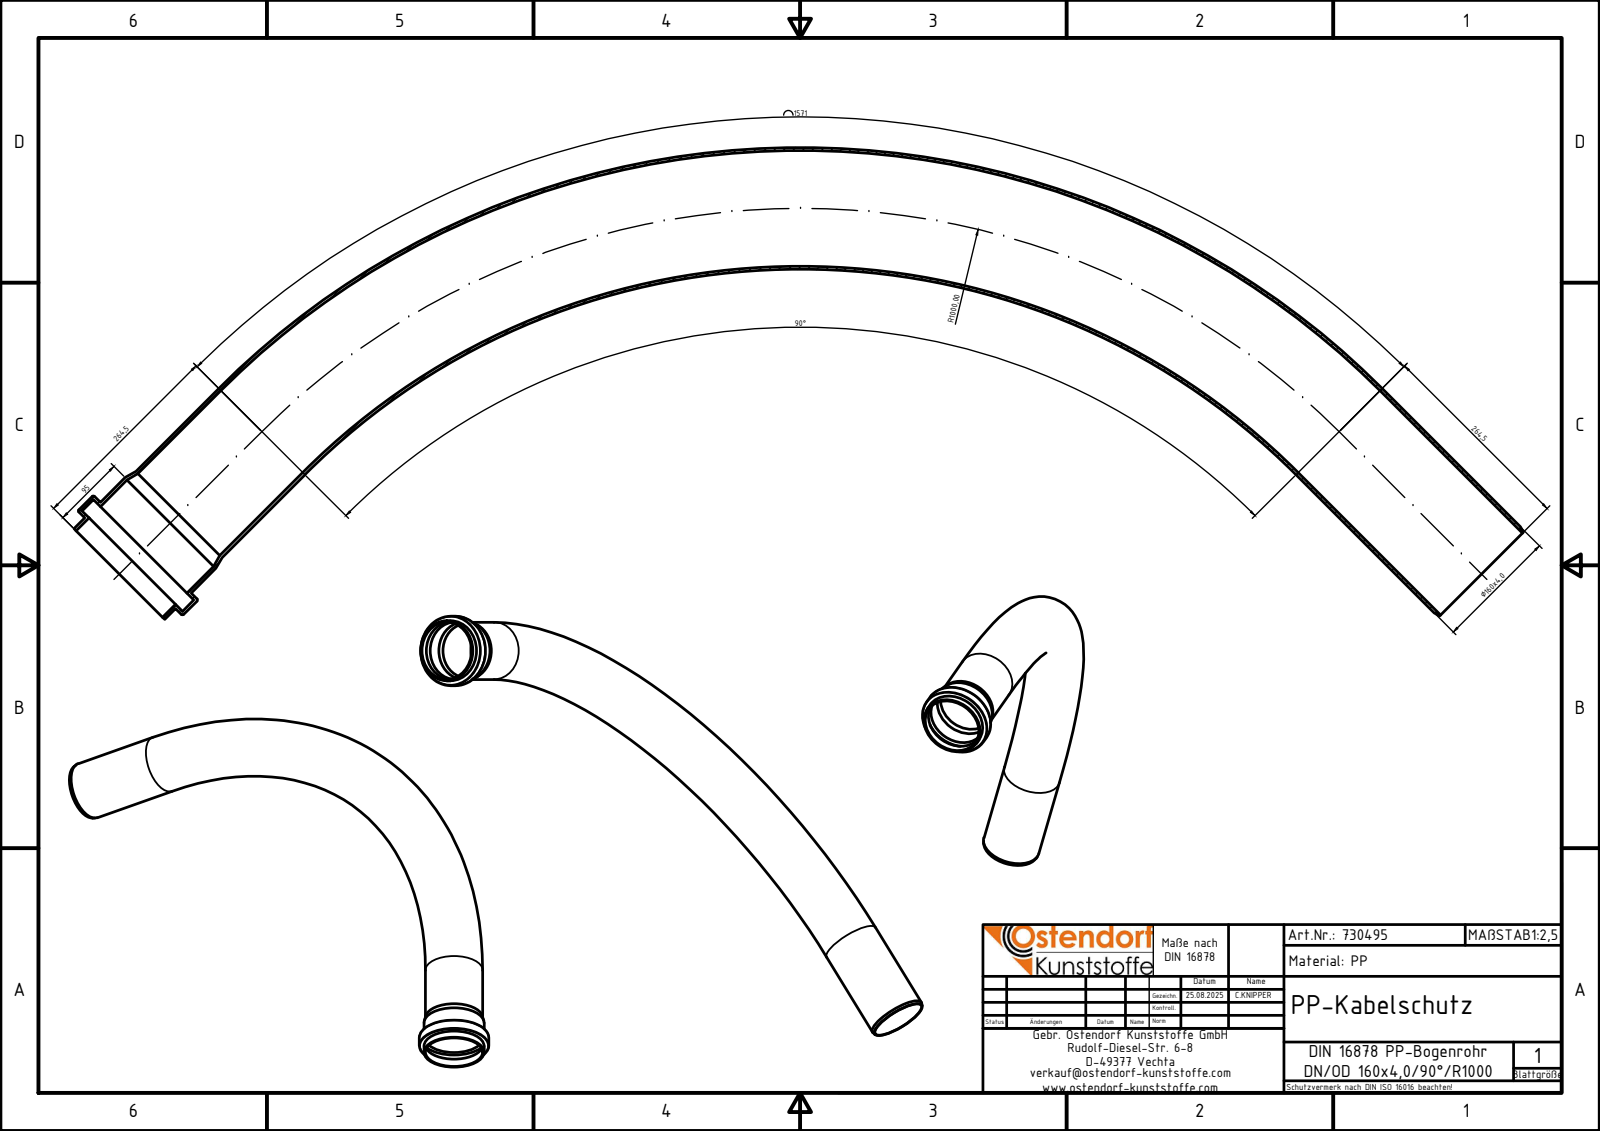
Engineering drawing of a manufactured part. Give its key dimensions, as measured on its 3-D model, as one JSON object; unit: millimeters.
{"part_name": "730495z", "step_written_by": "Autodesk Inventor 2024 (AUTOMOTIVE_DESIGN)", "units": "millimeters", "bodies": {"solids": 1, "faces": 23, "planar": 6, "cylindrical": 10, "other": 7}, "overall_size": [1902.9, 619.5, 194.5], "volume_mm3": 4189000, "surface_area_mm2": 2099000, "round_holes": [[152, 2], [160.5, 2], [186.5, 1]], "round_bosses_or_shafts": [[168.5, 2], [160, 2], [194.5, 1]], "face_to_face_distances": [4, 24.99, 20.99, 28.99, 20, 24, 44.99, 48.99]}
